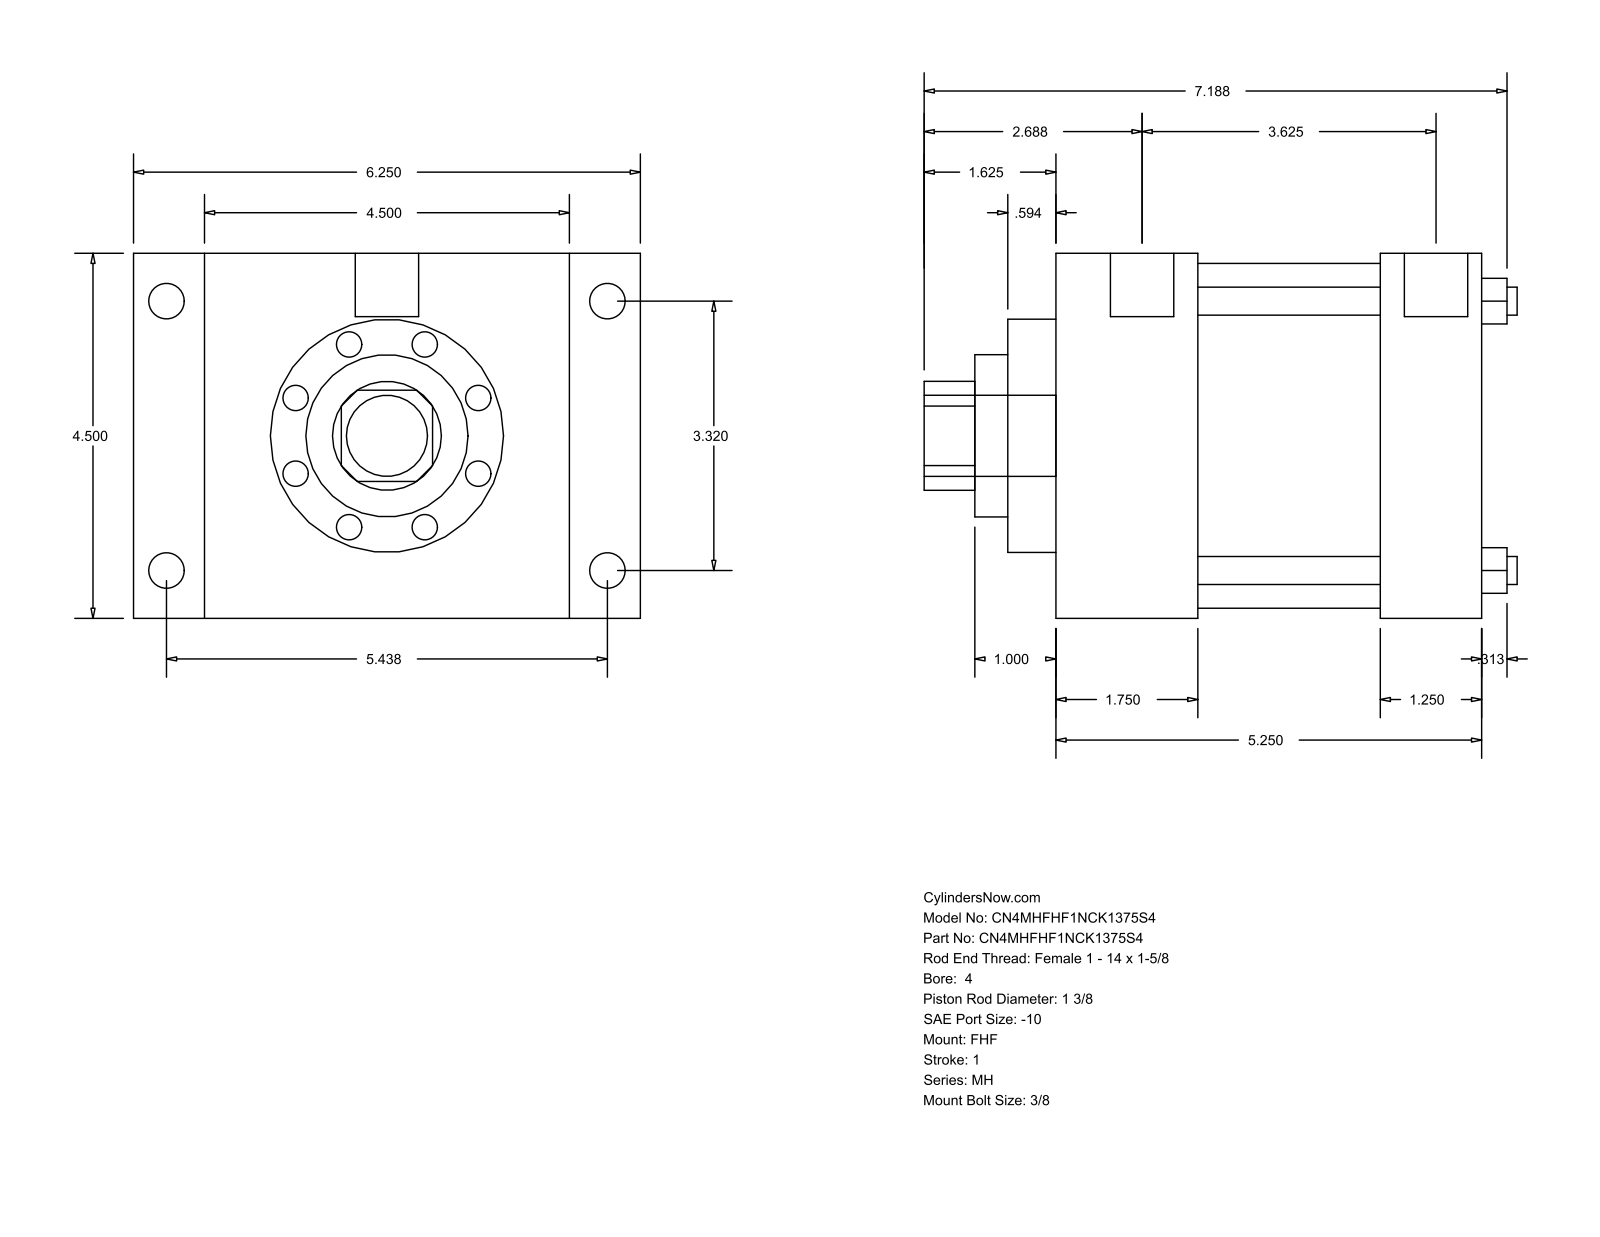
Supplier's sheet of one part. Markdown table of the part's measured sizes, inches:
| quantity | value |
| --- | --- |
| part name | MH_FHF__0400_1.375 |
| STEP written by | GSSL Pune (CONFIG_CONTROL_DESIGN) |
| units | inches |
| bodies | 0 solids, 90 faces (61 planar, 29 cylindrical, 0 other) |
| overall size | 7.313 × 6.25 × 4.5 |
| round holes (diameter × count) | 0.345 × 4, 1.375 × 1, 2 × 1, 2.875 × 1, 4.25 × 1 |
| round bosses / shafts (diameter × count) | 0.438 × 4, 0.344 × 4, 0.781 × 2, 1 × 1 |
| partial cylindrical surfaces (radius × count) | 0.672 × 1 |
| main face-to-face distances | 4.5, 5.25, 1.75, 3.5, 0.875, 5.375, 6.25, 4, 2.25, 1.25 |
| hole center spacings | 2.347, 3.32, 4.695 |
